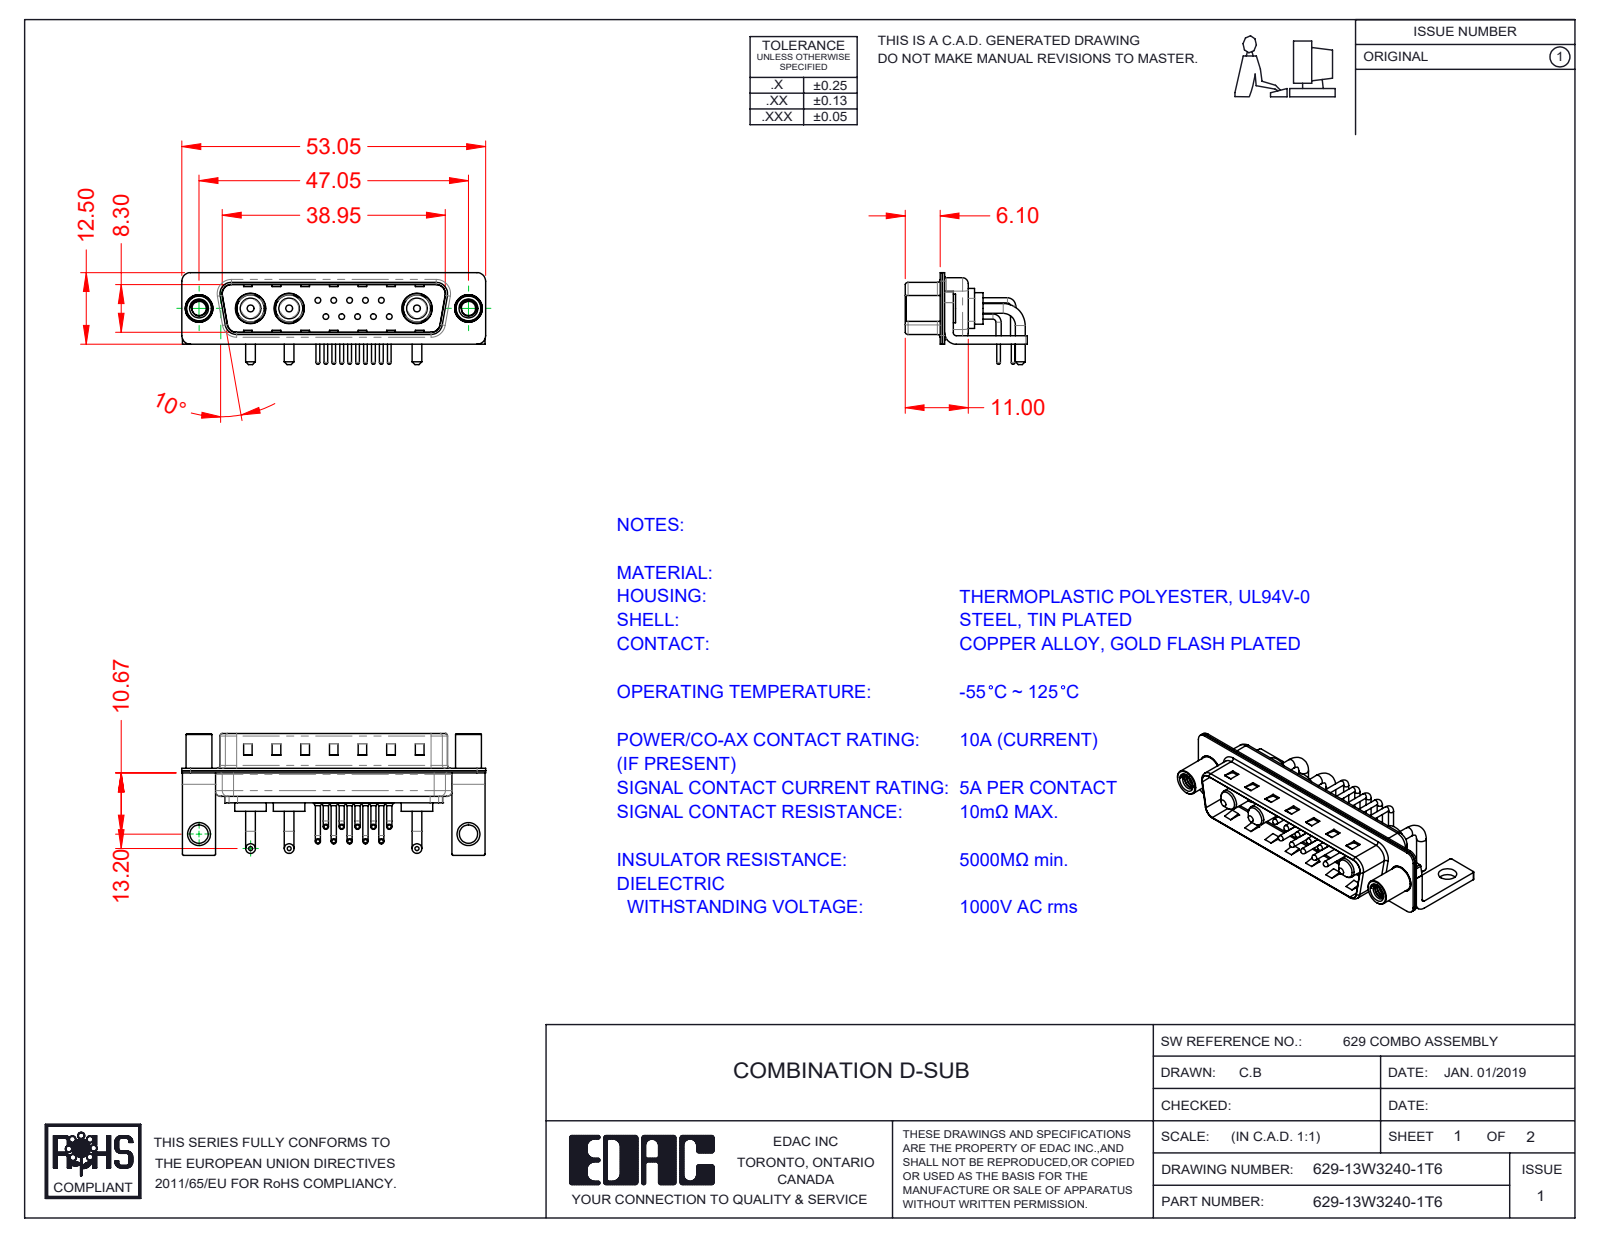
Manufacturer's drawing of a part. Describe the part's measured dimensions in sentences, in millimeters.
The part is named "Power Pin_10A RA; 629-13W3240-1T6; 629Combo Shell Rear_25 Contacts; 629Combo Shell Front_25 Contacts (+5 more)". Its 3-D file was written by "SolidWorks 2020 (CONFIG_CONTROL_DESIGN)". It is 23 solids with 1703 faces: 863 planar, 632 cylindrical and 208 other. Overall it measures 53.05 by 21.3 by 16.05 millimeters. Its volume is 3 420 cubic millimeters and its surface area 8 143 square millimeters. Round holes: 10 of diameter 0.75, 10 of diameter 1.6, 10 of diameter 2, 3 of diameter 4.85, 3 of diameter 5.3, 2 of diameter 2.5, 2 of diameter 3.2, 2 of diameter 4, 2 of diameter 4.8. Round bosses or shafts: 20 of diameter 0.9, 10 of diameter 1.5, 10 of diameter 1, 10 of diameter 0.65, 6 of diameter 1.7, 3 of diameter 5.5, 3 of diameter 5.2, 3 of diameter 4.75. Partial cylindrical surfaces (rounded edges, fillets, slot ends): 16 of radius 0.25, 16 of radius 1.5, 13 of radius 2, 10 of radius 1.01, 9 of radius 0.5, 8 of radius 1.6, 4 of radius 0.6, 4 of radius 0.65. The main face-to-face distances are 0.4, 0.8, 1.5, 9.5, 9.1, 8.7, 9.9, 5.2, 5.6, 0.6. The hole center spacings are 3.16, 2.77, 5.04, 5.54, 7.49, 5.03, 8.31, 10.11.
